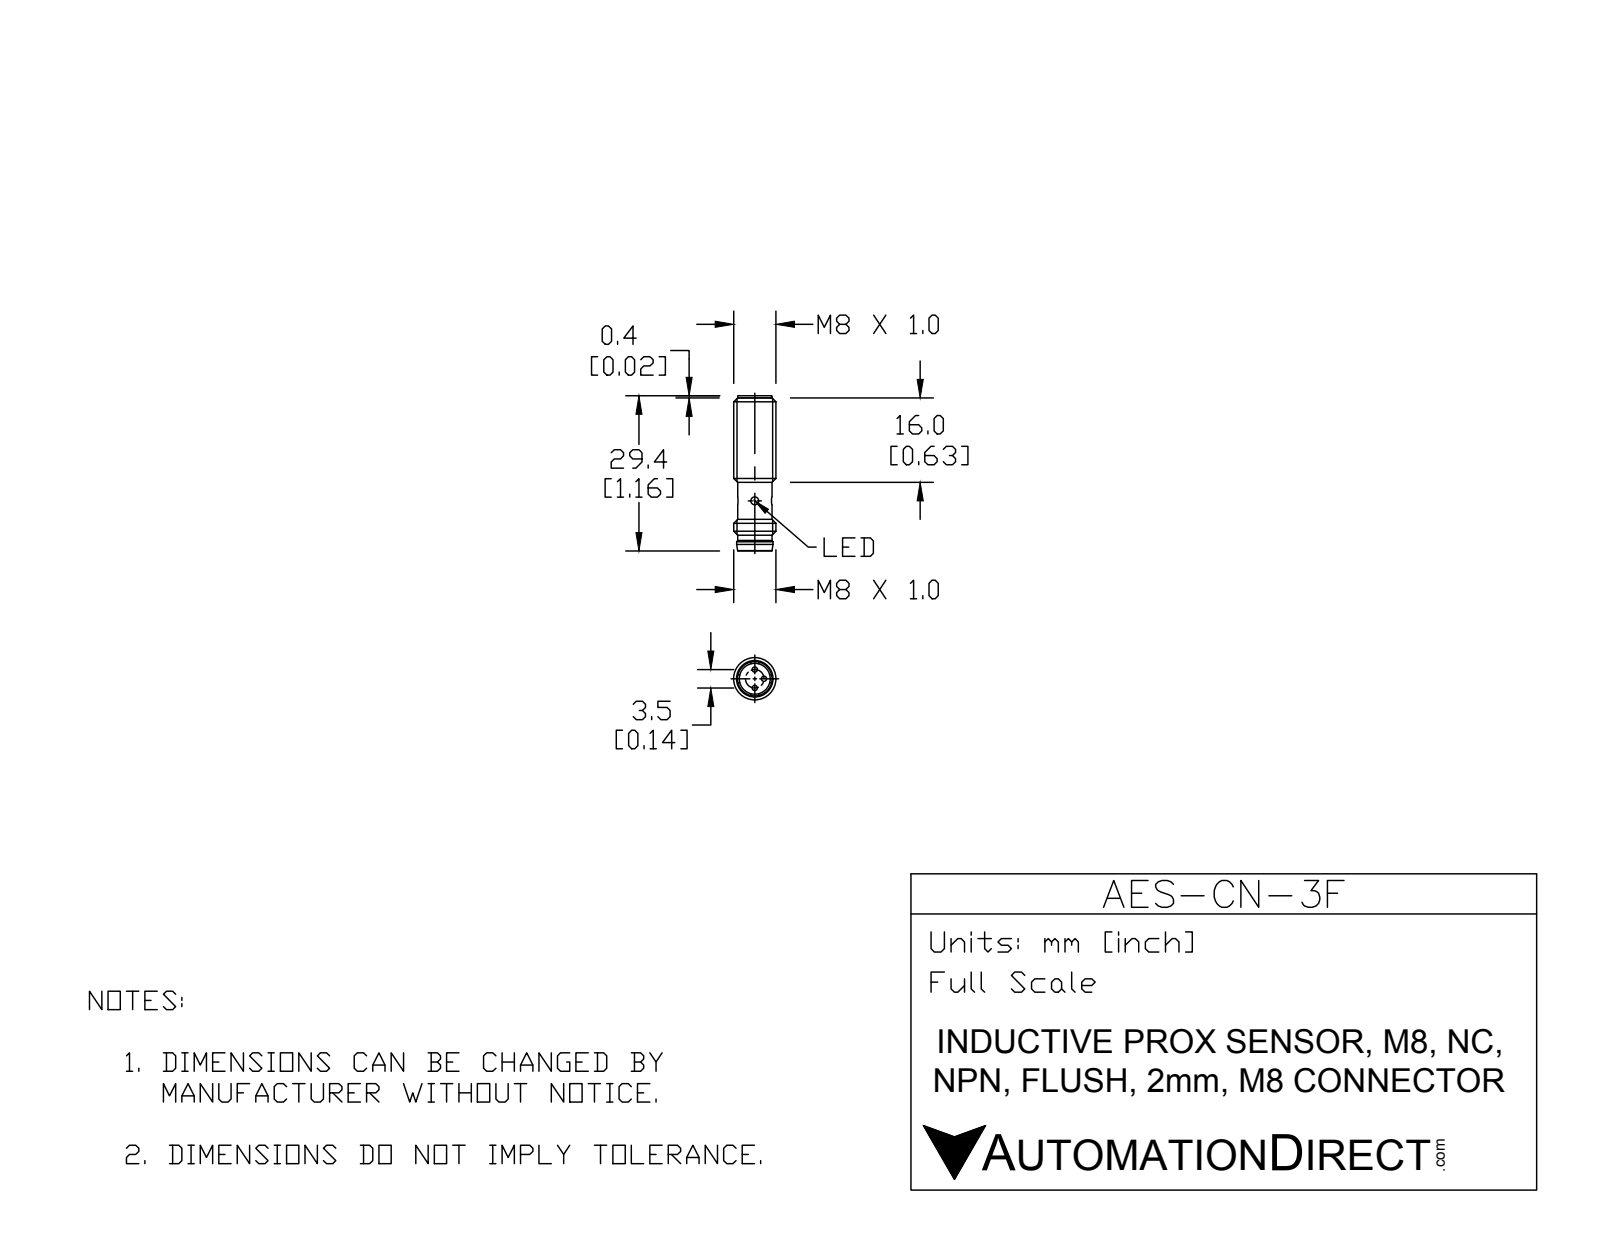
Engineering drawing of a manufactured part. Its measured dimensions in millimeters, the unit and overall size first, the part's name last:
Units: millimetres
Overall size (bounding box): 29.4 × 8 × 8
Round holes (diameter × count): ⌀1.5 ×2, ⌀5.85 ×1
Round bosses / shafts (diameter × count): ⌀1 ×3, ⌀8 ×1, ⌀6.9 ×1, ⌀6.5 ×1
Main face-to-face distances: 24.4, 3, 27.4, 5.5, 11, 8, 16.4, 27, 24, 16
Volume: 1 157 mm³ · Surface area: 928 mm²
Bodies: 1 solid, 58 faces (10 planar, 28 cylindrical, 20 other)
Part name (STEP PRODUCT): AES-CN-3F
STEP written by: SolidWorks 2015 (CONFIG_CONTROL_DESIGN)
